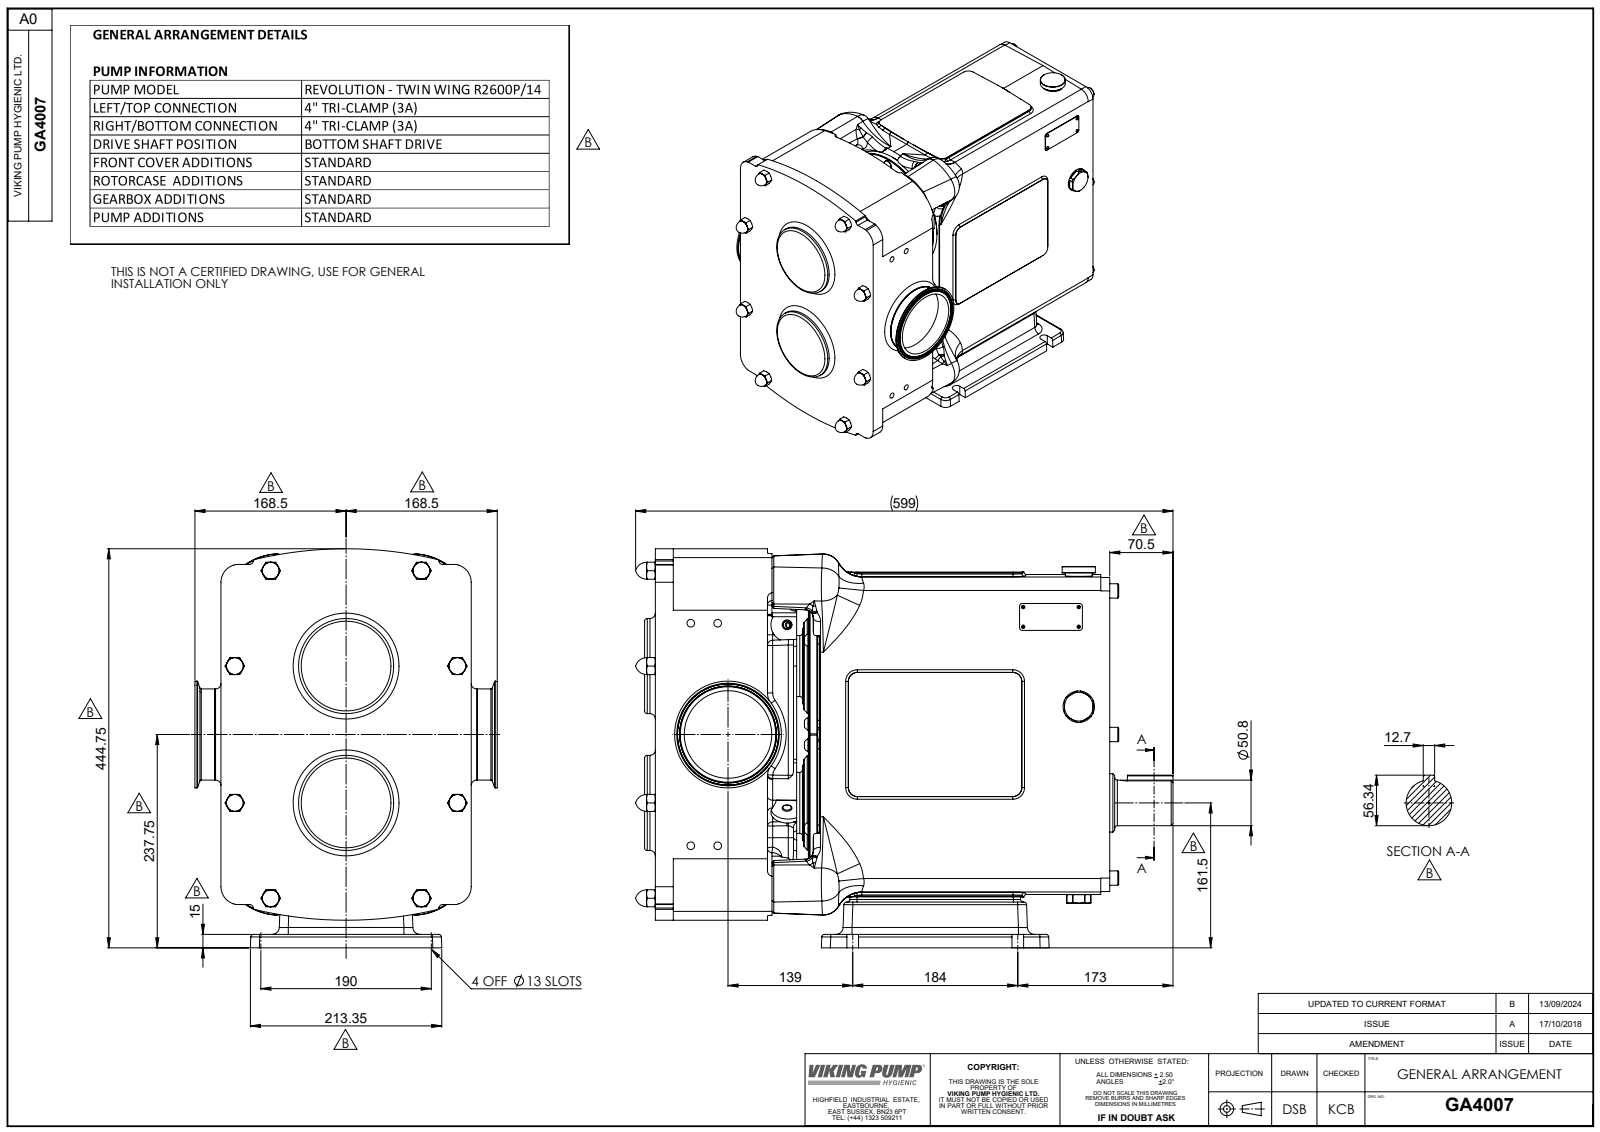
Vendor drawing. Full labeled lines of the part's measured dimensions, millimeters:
Part name (STEP PRODUCT): Copy of RA94-5121-66M^GA4007; GA4007; Copy of R2600 CPP H BSD^GA4007
STEP written by: SolidWorks 2023 (AUTOMOTIVE_DESIGN)
Units: millimetres
Bodies: 3 solids, 1582 faces (447 planar, 400 cylindrical, 735 other)
Overall size (bounding box): 599 × 444.75 × 337
Volume: 41 000 000 mm³ · Surface area: 1 201 000 mm²
Round holes (diameter × count): ⌀6 ×4, ⌀8.5 ×4, ⌀149 ×2, ⌀35 ×1, ⌀97.55 ×1
Round bosses / shafts (diameter × count): ⌀14 ×10, ⌀8 ×10, ⌀16 ×6, ⌀18 ×4, ⌀187 ×2, ⌀140 ×2, ⌀106 ×2, ⌀85 ×2
Partial cylindrical surfaces — rounded edges, fillets, slot ends (radius × count): R3 ×44, R6 ×44, R10 ×28, R0.2 ×24, R5 ×16, R8 ×10, R15 ×8, R20 ×6
Main face-to-face distances: 193, 190, 506.5, 3, 41.5, 237.5, 44.5, 234.5, 349, 157.5
Hole centre spacings: 30, 78.37, 108.36, 124.53, 130.76, 139.33, 248, 249.81
